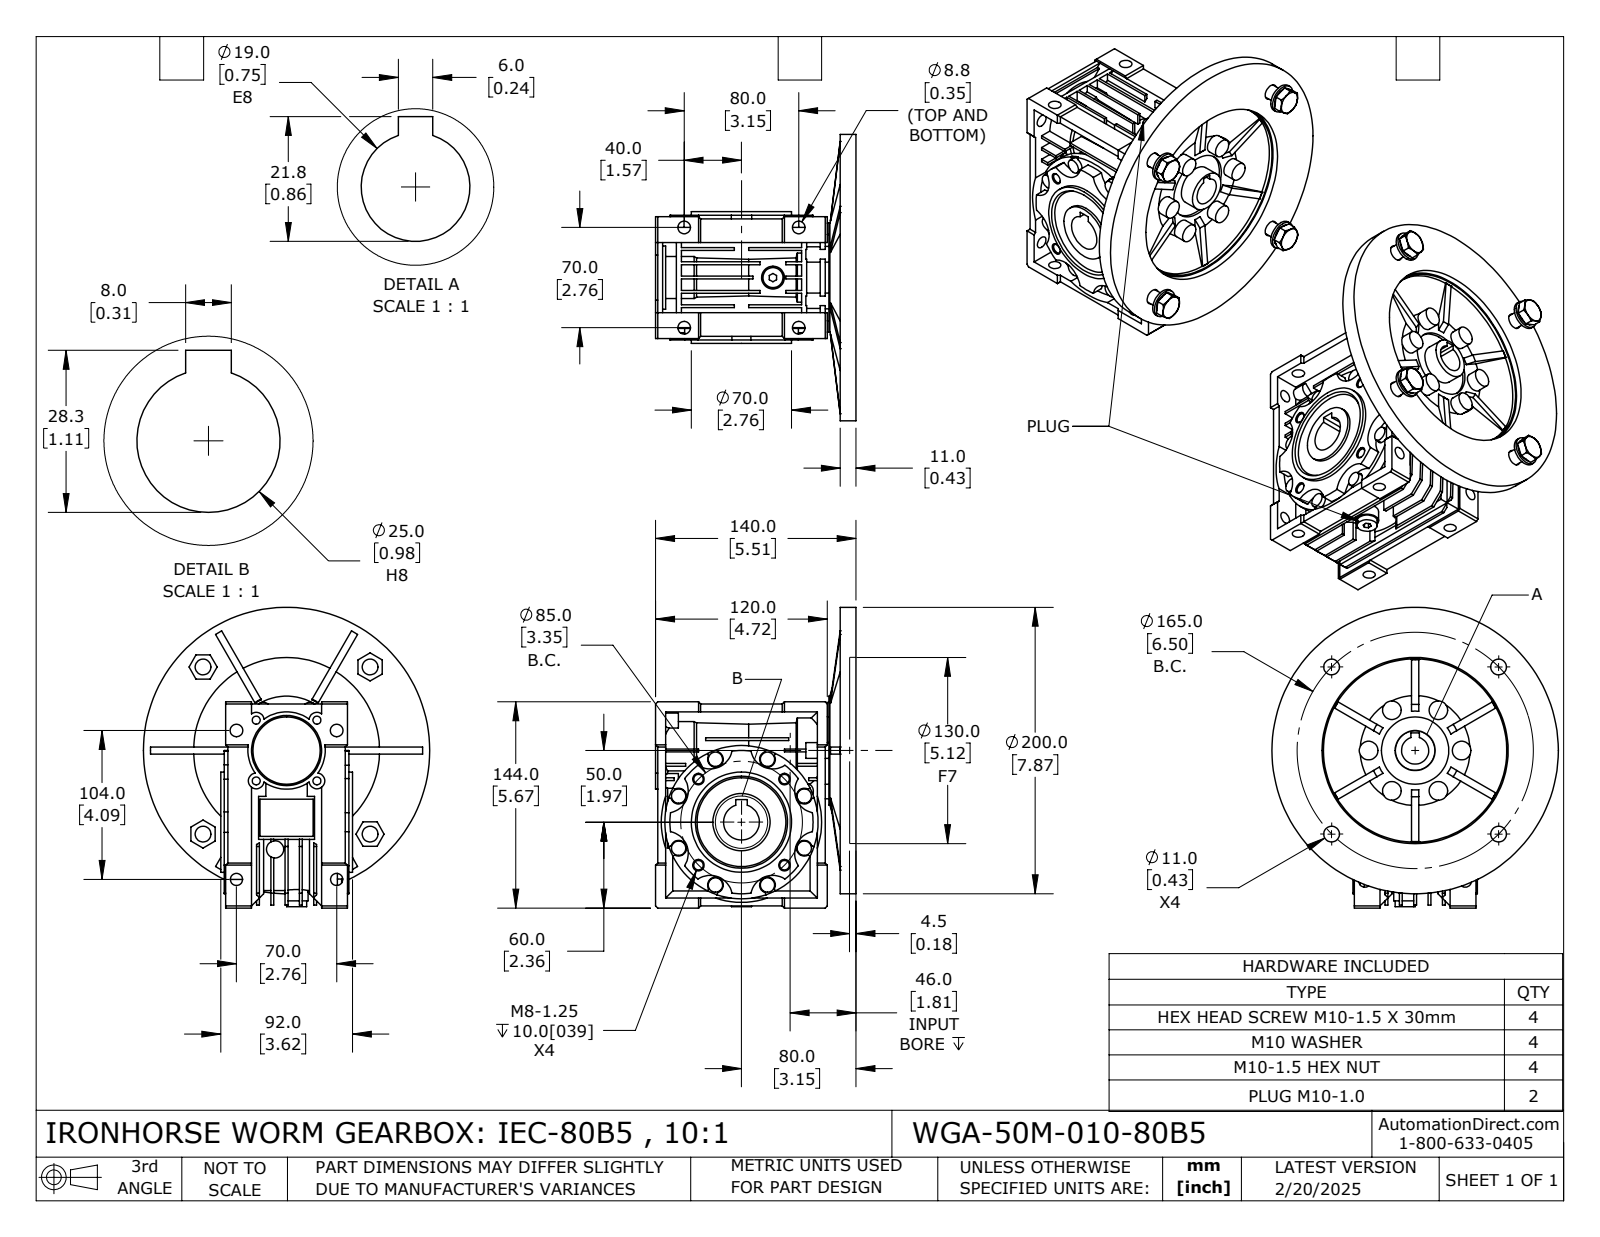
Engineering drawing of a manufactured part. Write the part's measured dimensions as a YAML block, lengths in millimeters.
part_name: "WGA-50M-010-80B5"
step_written_by: "SolidWorks 2024 (CONFIG_CONTROL_DESIGN)"
units: millimeters
bodies: {solids: 19, faces: 1273, planar: 701, cylindrical: 364, other: 208}
overall_size: [210, 200, 158.43]
volume: 1274000
surface_area: 298738
round_holes:
  - {diameter: 8.5, count: 10}
  - {diameter: 8.8, count: 8}
  - {diameter: 5.55, count: 4}
  - {diameter: 10, count: 4}
  - {diameter: 10.5, count: 4}
  - {diameter: 11, count: 4}
  - {diameter: 6.65, count: 2}
  - {diameter: 6.65, count: 2}
  - {diameter: 9, count: 2}
  - {diameter: 19, count: 1}
  - {diameter: 20, count: 1}
  - {diameter: 25, count: 1}
round_bosses_or_shafts:
  - {diameter: 10, count: 8}
  - {diameter: 16, count: 6}
  - {diameter: 13, count: 6}
  - {diameter: 20, count: 4}
  - {diameter: 14, count: 2}
  - {diameter: 9.8, count: 2}
  - {diameter: 8.3, count: 2}
  - {diameter: 200, count: 1}
partial_cylinders:
  - {radius: 5.5, count: 18}
  - {radius: 6, count: 8}
  - {radius: 15, count: 8}
  - {radius: 15.5, count: 8}
  - {radius: 20.76, count: 1}
  - {radius: 46, count: 1}
  - {radius: 47.7, count: 1}
  - {radius: 50, count: 1}
face_to_face_distances: [11, 8, 10, 2, 1.5, 7, 5.5, 20, 5, 55]
hole_center_spacings: [87.79, 70, 30, 42.42, 42.5, 52.51, 60.1, 82.51]
